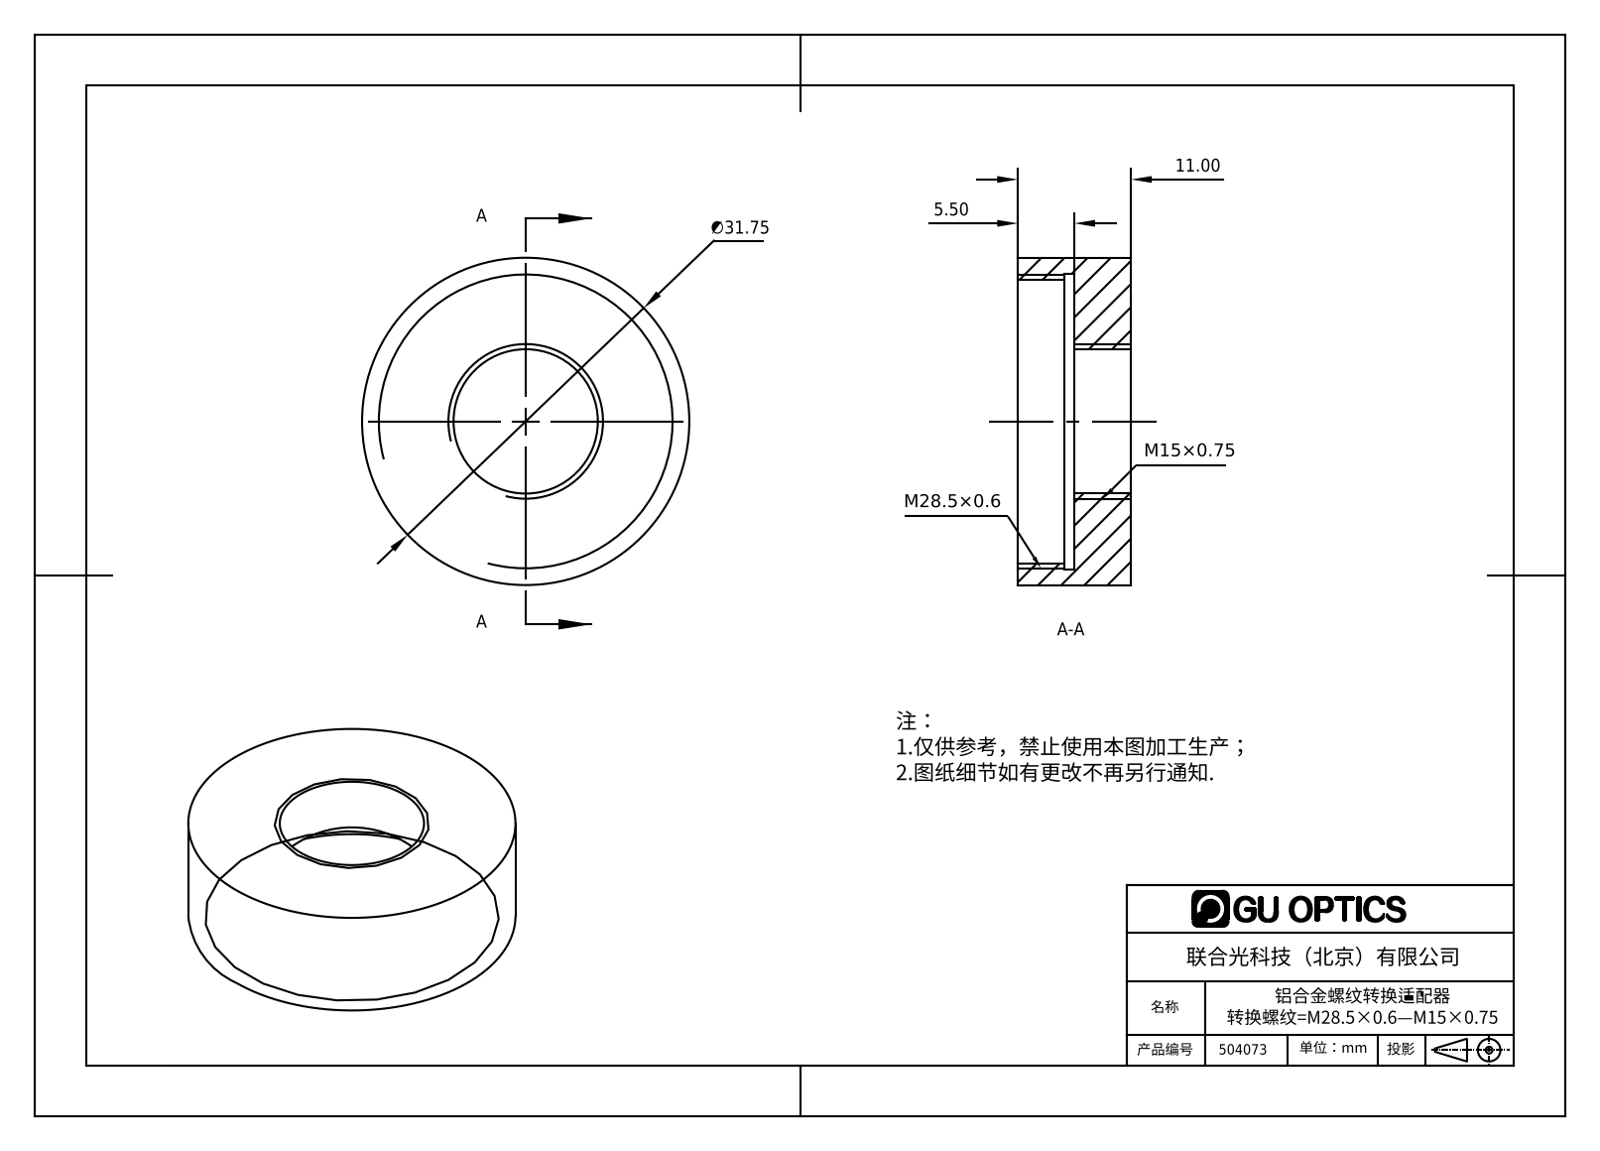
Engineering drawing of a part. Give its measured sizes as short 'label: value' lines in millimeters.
name: 504073
written by: SolidWorks 2016 (AUTOMOTIVE_DESIGN)
unit: mm
bodies: 1 solid, 12 faces (4 planar, 8 cylindrical, 0 other)
size: 31.75 × 31.75 × 11
volume: 4 543 mm³; area: 3 200 mm²
holes: 1× ⌀14, 1× ⌀27.5, 1× ⌀28.7
bosses: 1× ⌀31.75
face distances: 5.5, 11, 4.5, 1, 6.5
